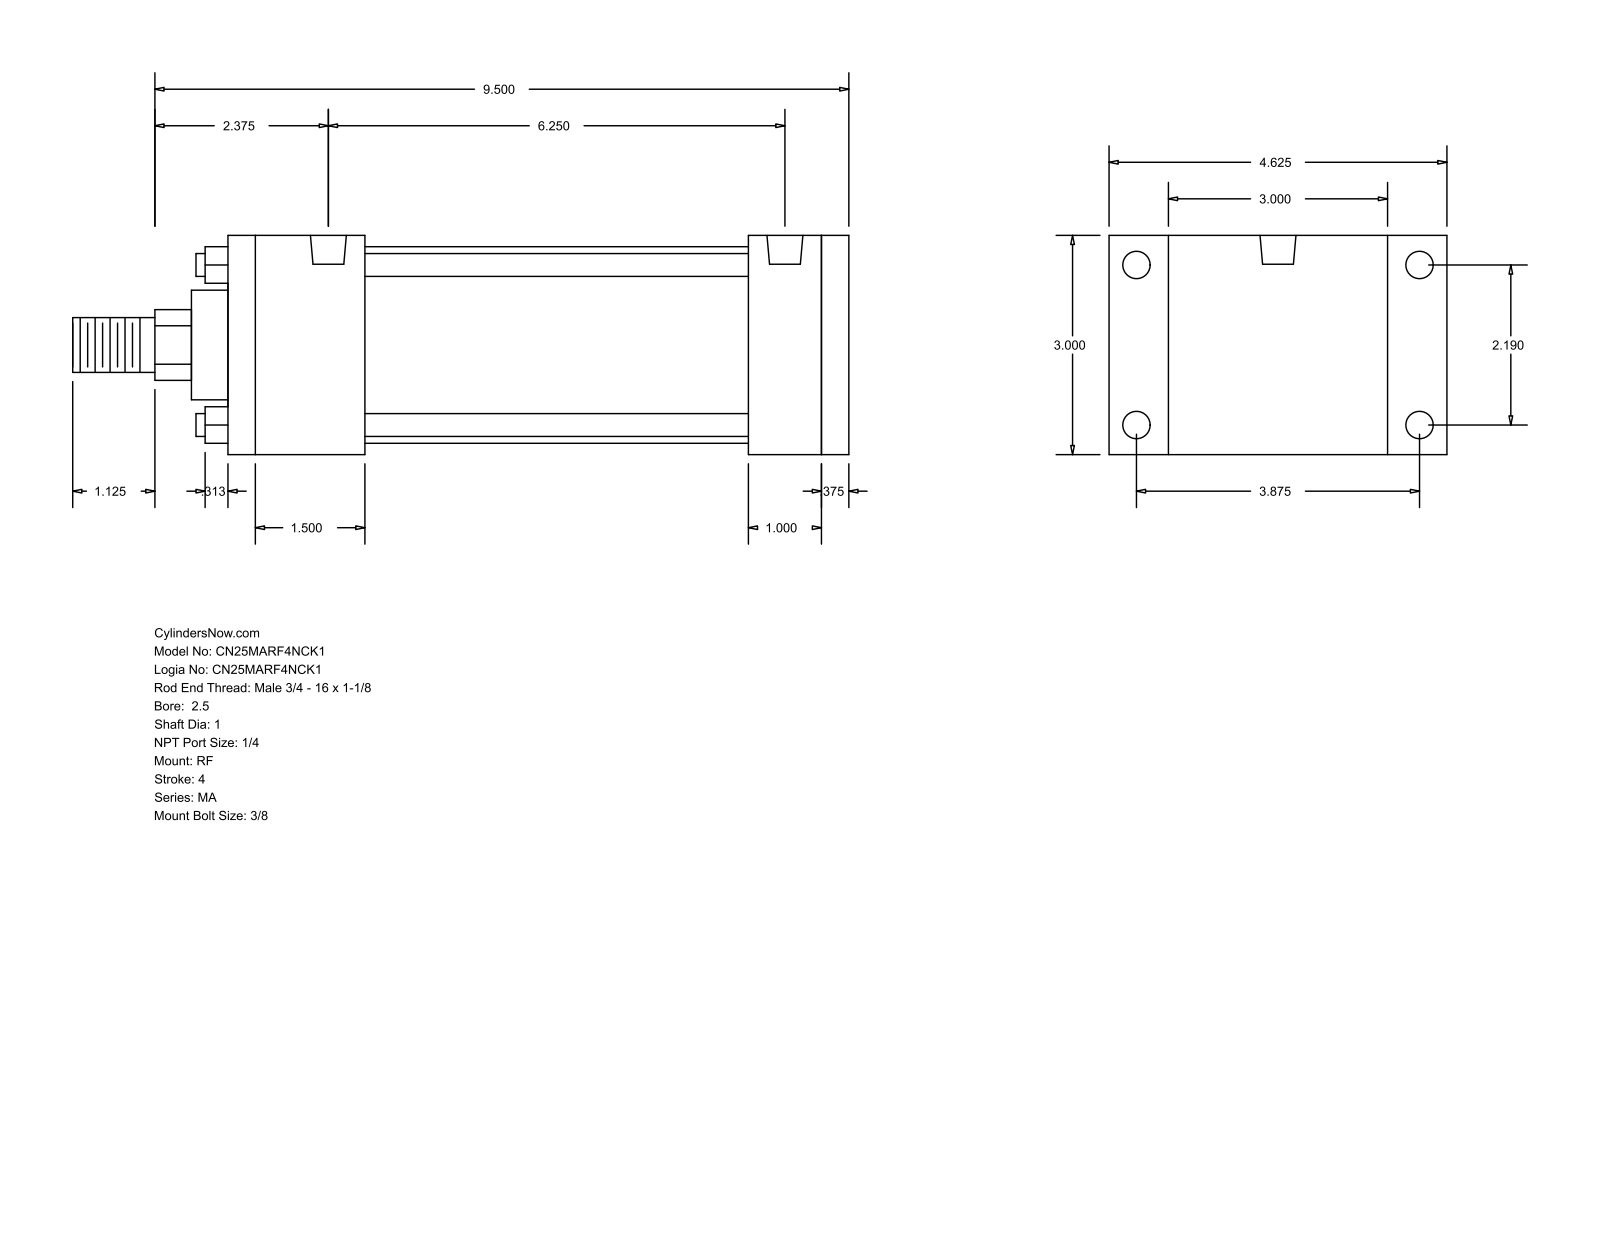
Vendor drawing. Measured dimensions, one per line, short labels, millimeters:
name: MA_RF__0250_1
written by: GSSL Pune (CONFIG_CONTROL_DESIGN)
unit: mm
bodies: 0 solids, 92 faces (64 planar, 28 cylindrical, 0 other)
size: 269.88 × 117.47 × 76.2
holes: 4× ⌀7.94, 4× ⌀9.53, 2× ⌀12.49
bosses: 4× ⌀7.94, 1× ⌀68.33, 1× ⌀38.1, 1× ⌀25.4, 1× ⌀19.05
rounds: 1× R12.29
face distances: 76.2, 215.9, 206.38, 9.52, 25.4, 47.63, 180.98, 133.35, 158.75, 168.27
hole spacings: 55.62, 98.42, 113.05, 158.74
